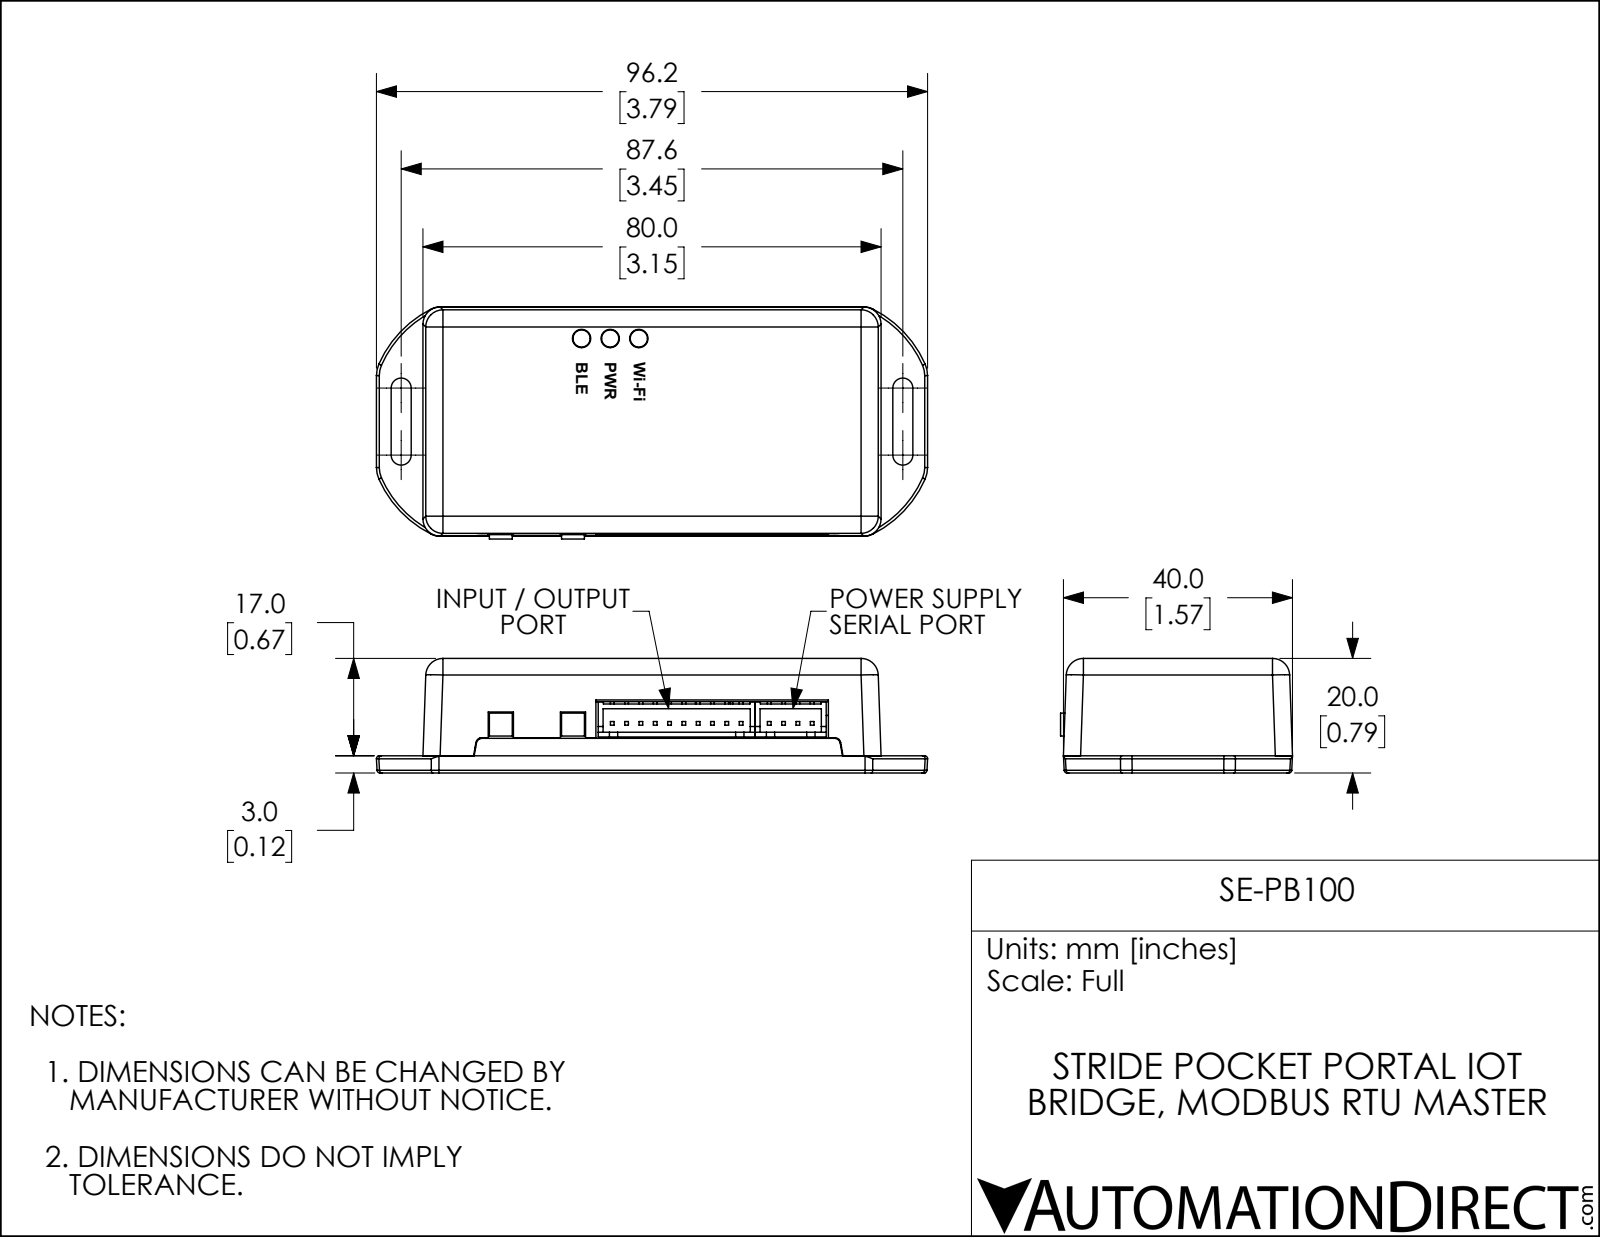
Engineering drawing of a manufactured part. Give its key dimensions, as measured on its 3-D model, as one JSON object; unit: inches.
{"part_name": "SE-PB100", "step_written_by": "SolidWorks 2018 (AUTOMOTIVE_DESIGN)", "units": "inches", "bodies": {"solids": 5, "faces": 499, "planar": 358, "cylindrical": 86, "other": 55}, "overall_size": [3.789, 1.594, 0.787], "volume_in3": 1.663, "surface_area_in2": 47.21, "round_holes": [[0.126, 5], [0.055, 2], [0.067, 2], [0.098, 2], [0.102, 2], [0.138, 2]], "round_bosses_or_shafts": [[0.118, 3], [0.209, 2], [0.197, 2], [0.157, 2], [0.051, 2]], "partial_cylinders_radius": [[0.039, 12], [0.118, 8], [0.02, 6], [0.069, 6], [0.024, 2], [0.049, 2]], "face_to_face_distances": [0.079, 0.709, 0.787, 0.63, 0.557, 0.478, 0.152, 0.23, 0.219, 0.411], "hole_center_spacings": [0.197, 0.167, 0.37, 0.394, 0.397, 0.854, 0.88, 1.051]}
